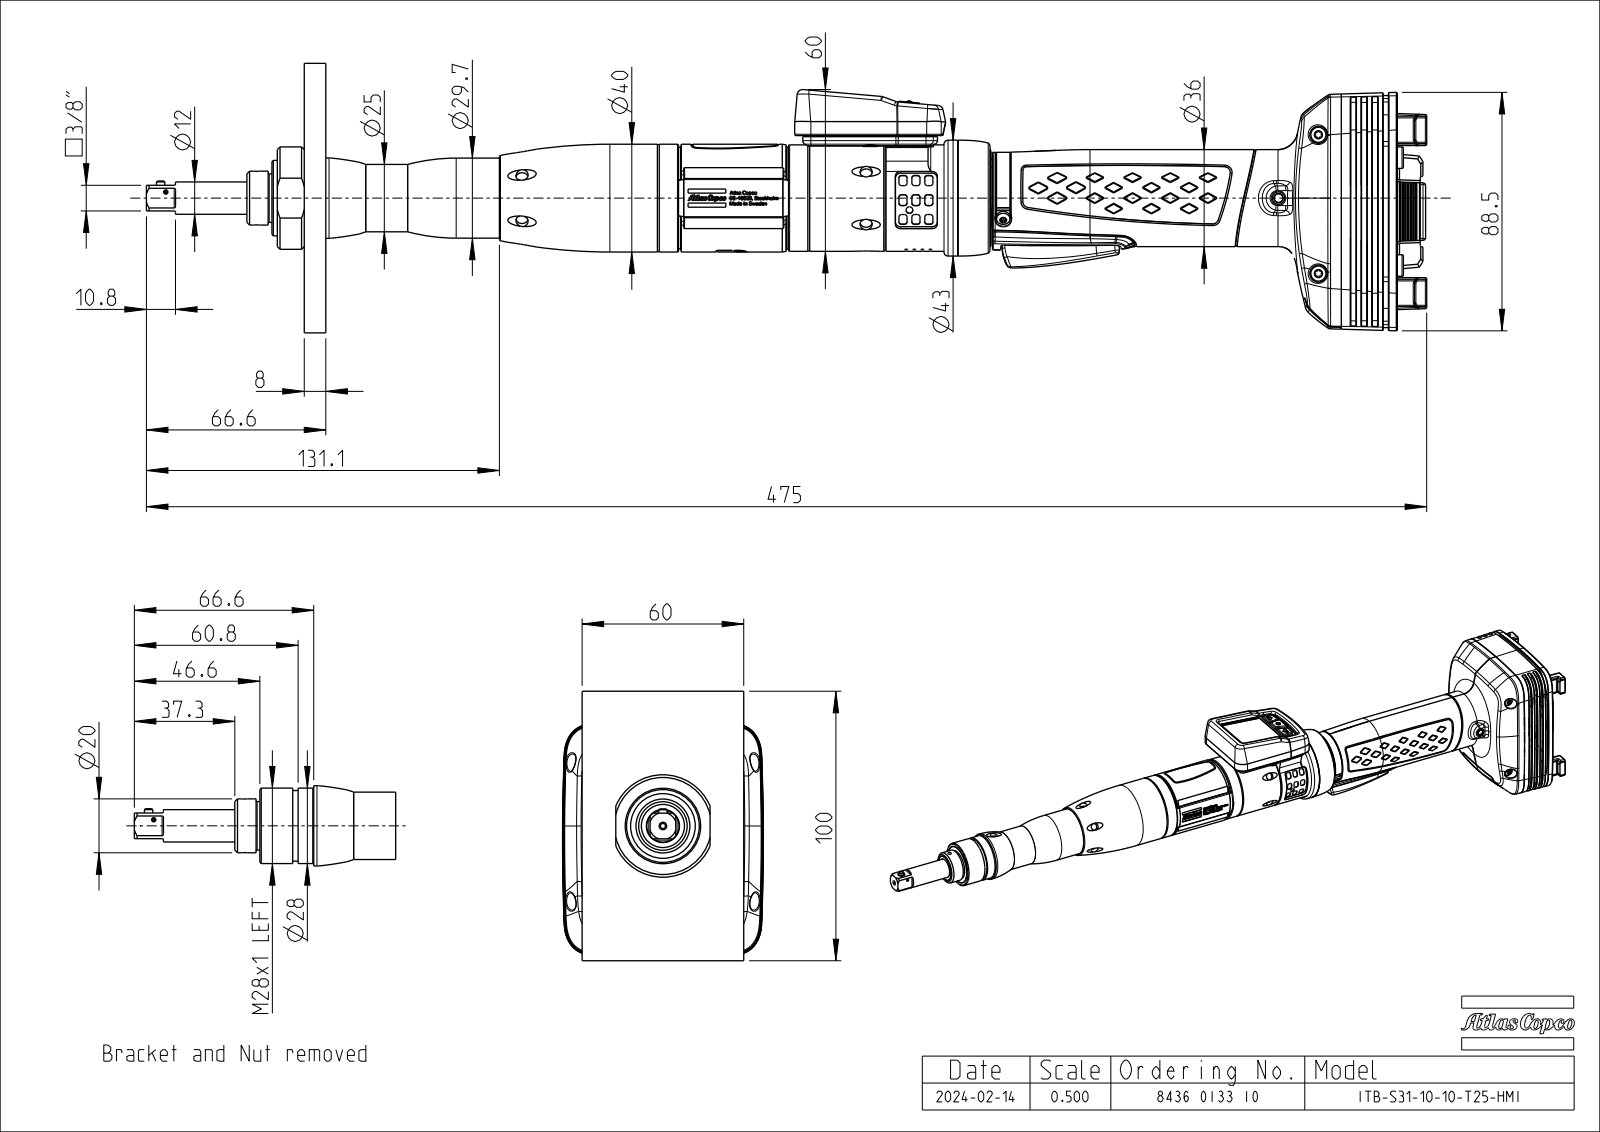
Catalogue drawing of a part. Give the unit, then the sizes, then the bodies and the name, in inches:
Units: inches
Overall size (bounding box): 18.713 × 3.525 × 2.934
Round holes (diameter × count): ⌀0.039 ×12, ⌀0.126 ×11, ⌀0.098 ×9, ⌀0.177 ×9, ⌀0.118 ×6, ⌀0.087 ×5, ⌀0.13 ×4, ⌀0.169 ×4, ⌀0.228 ×4, ⌀0.256 ×4, ⌀0.157 ×3, ⌀0.063 ×2
Round bosses / shafts (diameter × count): ⌀0.244 ×4, ⌀0.217 ×4, ⌀0.157 ×4, ⌀0.138 ×3, ⌀0.197 ×2, ⌀1.693 ×1, ⌀1.575 ×1, ⌀1.559 ×1
Partial cylindrical surfaces — rounded edges, fillets, slot ends (radius × count): R0.012 ×601, R0.02 ×248, R0.008 ×247, R0.039 ×127, R0.016 ×122, R0.079 ×106, R0.004 ×42, R0.012 ×31
Main face-to-face distances: 0.441, 0.079, 0.118, 0.795, 0.354, 1.346, 0.531, 0.087, 0.894, 0.433
Hole centre spacings: 0.118, 0.236, 0.75, 2.184, 2.294, 3.077, 0.354, 5.03
Volume: 28.39 in³ · Surface area: 290.2 in²
Bodies: 9 solids, 13666 faces (4777 planar, 2968 cylindrical, 5921 other)
Part name (STEP PRODUCT): EXT_COMP_SW0004
STEP written by: CREO PARAMETRIC BY PTC INC, 2020281 (CONFIG_CONTROL_DESIGN)
